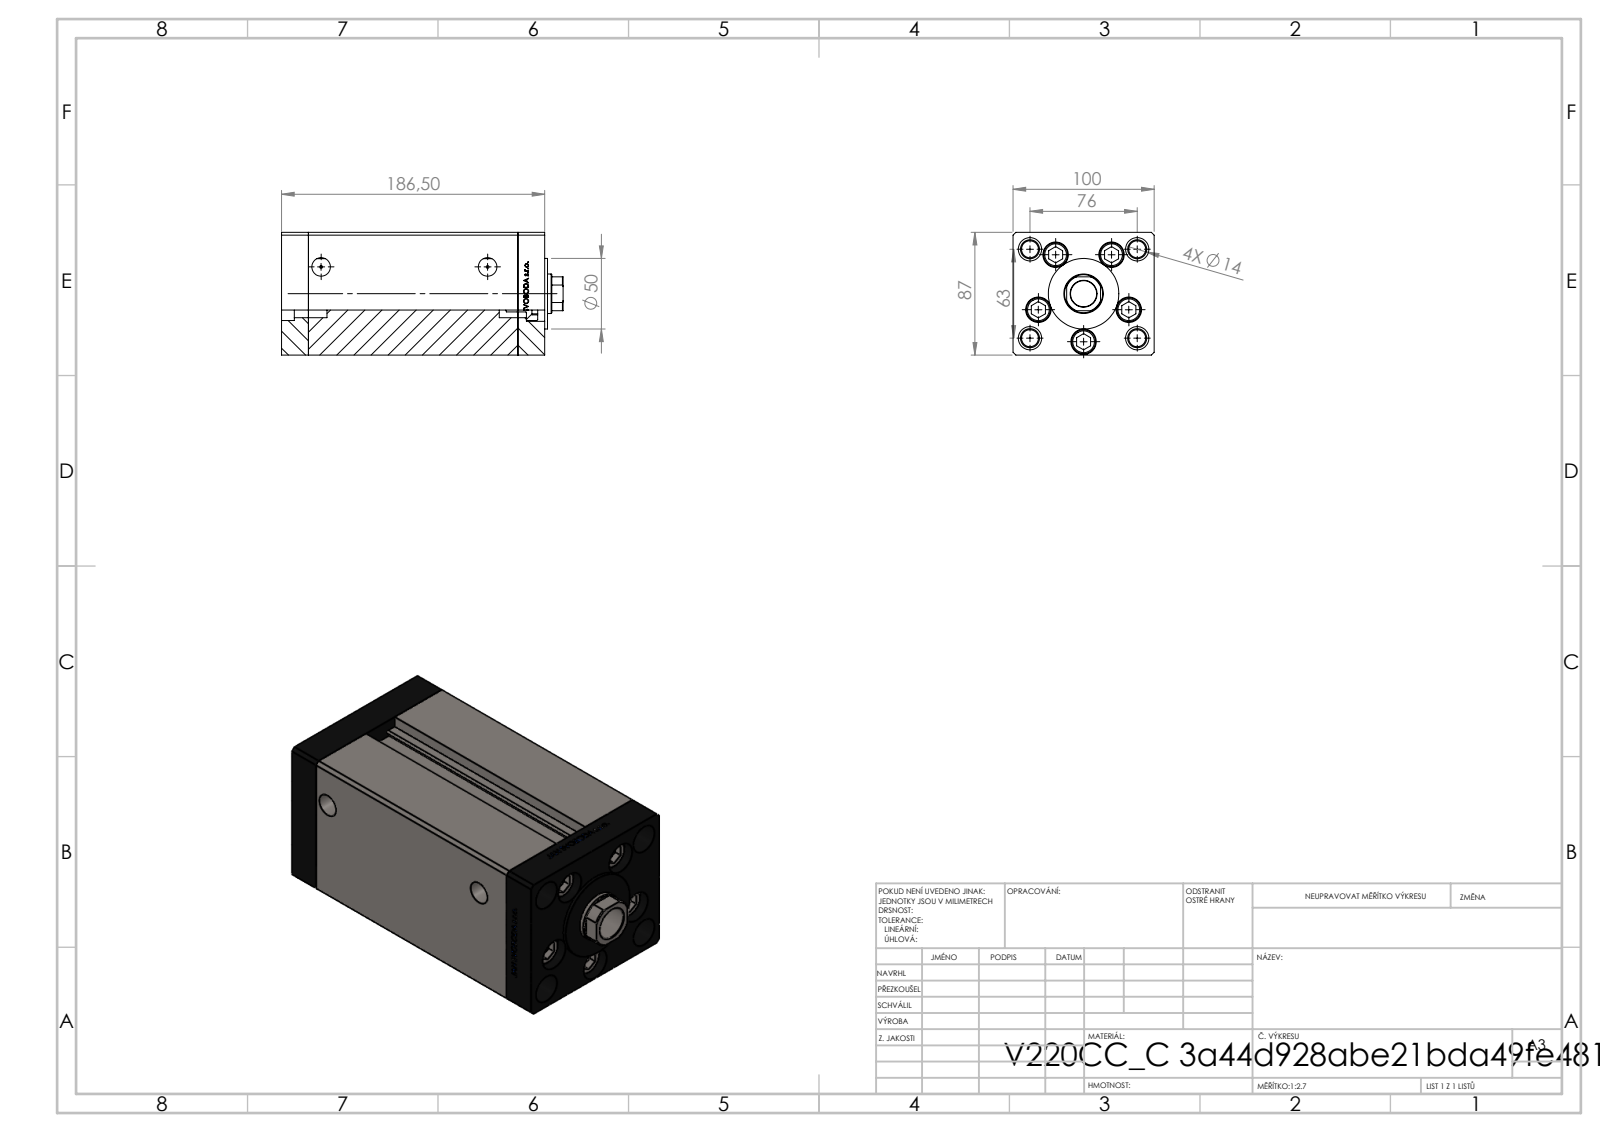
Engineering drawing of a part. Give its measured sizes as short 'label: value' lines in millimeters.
name: V220C FRONT; V220C_C MIDDLE; V220C BACK_C; ALLEN BOLT (+1 more)
written by: SolidWorks 2019 (CONFIG_CONTROL_DESIGN)
unit: mm
bodies: 13 solids, 1172 faces (542 planar, 168 cylindrical, 462 other)
size: 199.5 × 100 × 87
volume: 1 332 000 mm³; area: 229 693 mm²
holes: 9× ⌀13.5, 5× ⌀18, 4× ⌀12, 4× ⌀16.5, 2× ⌀2, 2× ⌀13.16, 1× ⌀17, 1× ⌀18.5, 1× ⌀28
bosses: 5× ⌀8, 4× ⌀17, 1× ⌀50
rounds: 2× R0.93, 1× R13.5
face distances: 100, 87, 19, 148.5, 167.5, 34.25, 186.5, 152.25, 133.25, 15.25
hole spacings: 34, 49.36, 18.59, 21.03, 38.08, 39.27, 40.83, 43.24
